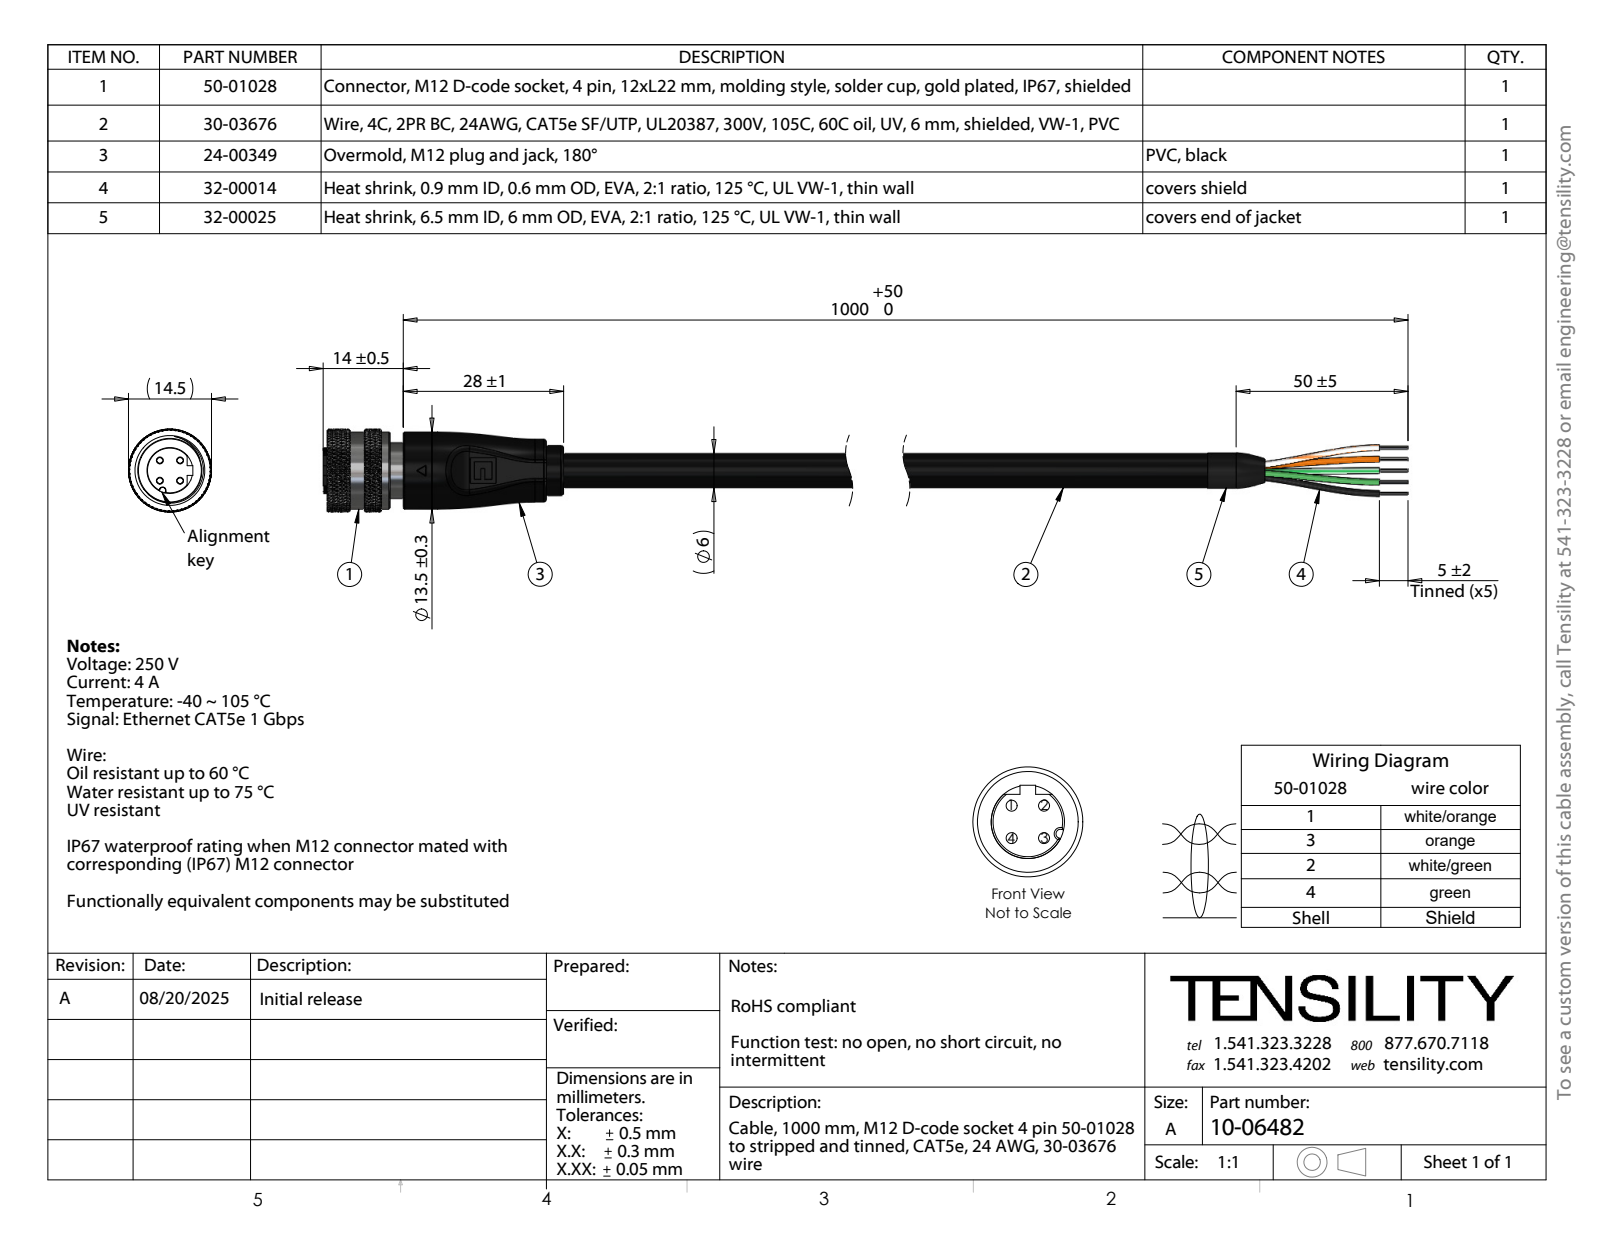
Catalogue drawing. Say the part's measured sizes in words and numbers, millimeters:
The part is named "30-03676_s + t; 50-01028-05_默认; 50-01028-04_默认; 24-00349_Mexico (+5 more)". Its 3-D file was written by "SolidWorks 2025 (CONFIG_CONTROL_DESIGN)". It is 87 solids with 3550 faces: 339 planar, 940 cylindrical and 2271 other. Overall it measures 222 by 14.5 by 14.5 millimeters. Its volume is 9 616 cubic millimeters and its surface area 27 027 square millimeters. Round holes: 28 of diameter 0.2, 4 of diameter 1.05, 4 of diameter 1.1, 4 of diameter 1.2, 1 of diameter 3.16, 1 of diameter 3.21, 1 of diameter 3.36, 1 of diameter 9, 1 of diameter 10, 1 of diameter 11.2. Round bosses or shafts: 35 of diameter 0.2, 4 of diameter 1.6, 4 of diameter 1.5, 1 of diameter 13.5, 1 of diameter 11, 1 of diameter 10.6, 1 of diameter 10.5, 1 of diameter 9.8. Partial cylindrical surfaces (rounded edges, fillets, slot ends): 10 of radius 0.1, 6 of radius 0.4, 2 of radius 0.5, 2 of radius 1.5, 1 of radius 4, 1 of radius 5, 1 of radius 5.58, 1 of radius 6.75. The main face-to-face distances are 178, 28, 150, 7, 4.7, 1, 31.8, 3.5, 23.3, 173.3. The hole center spacings are 1.91, 0.36, 2.09, 1.06, 0.89, 1.08, 1.24, 1.8.
